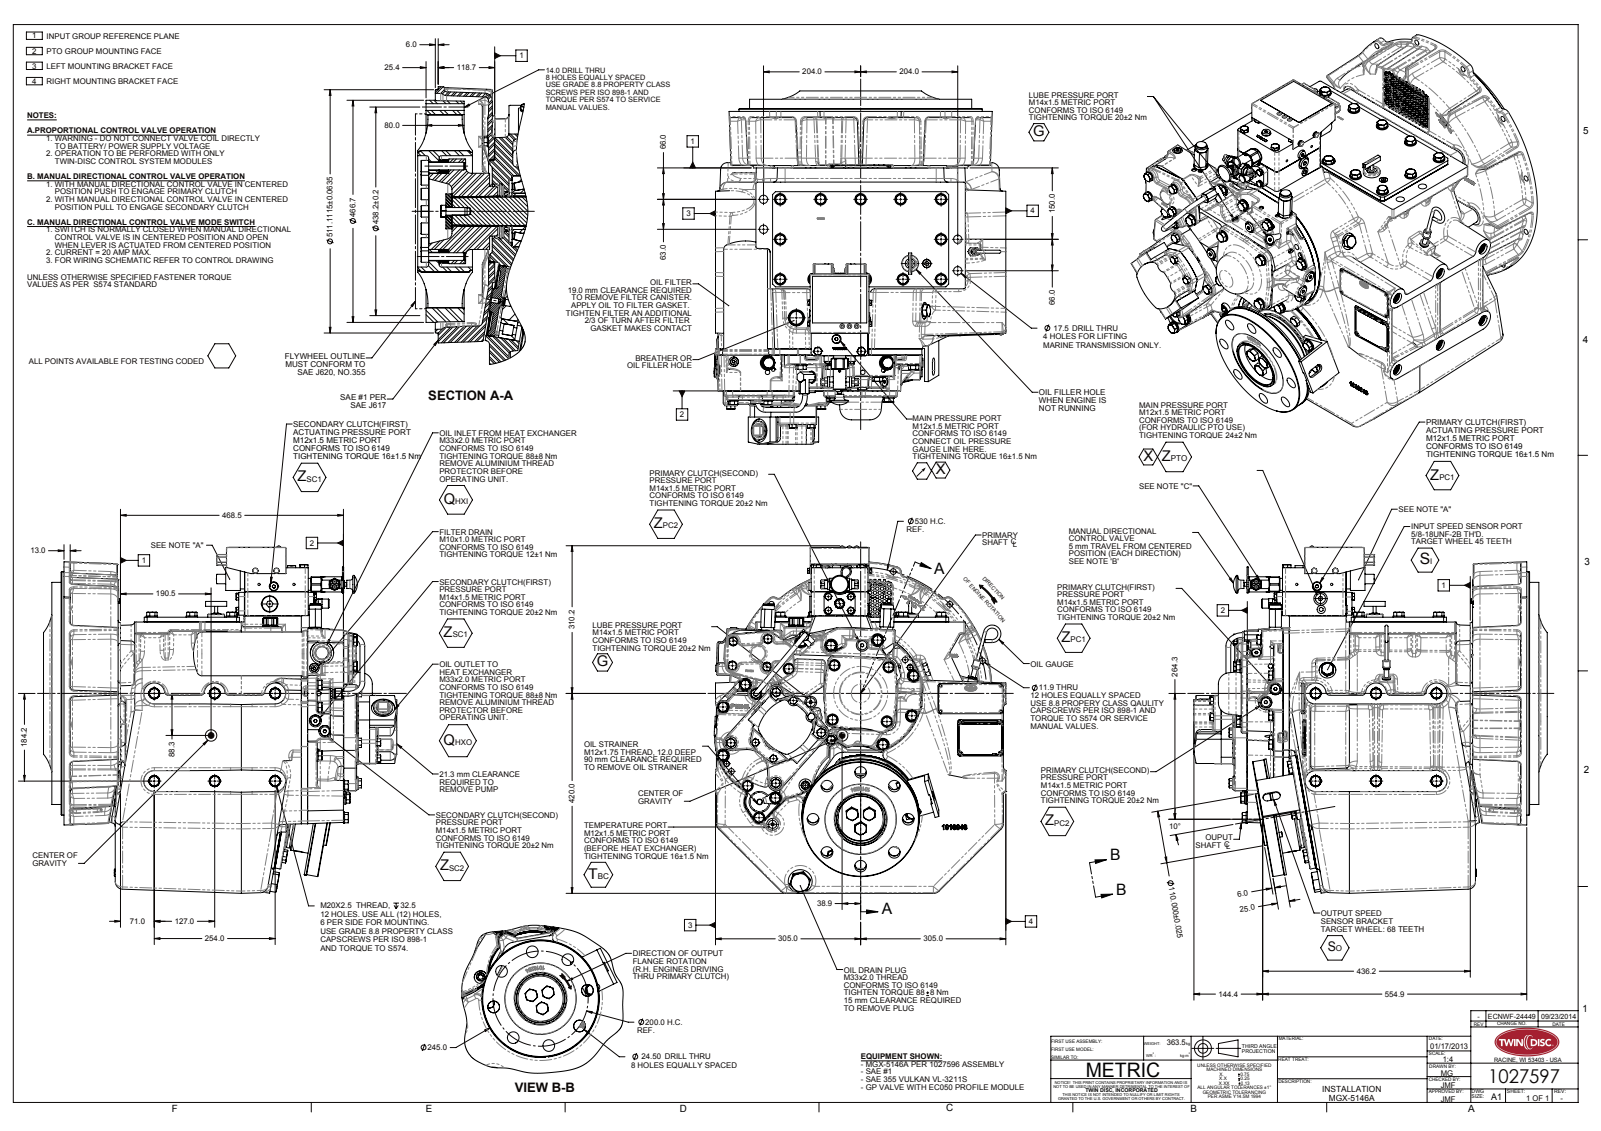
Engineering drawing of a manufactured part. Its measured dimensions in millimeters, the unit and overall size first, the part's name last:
Units: millimetres
Overall size (bounding box): 742.31 × 730.22 × 615.4
Round holes (diameter × count): ⌀7 ×74, ⌀11.91 ×12, ⌀14 ×12, ⌀13 ×10, ⌀12 ×8, ⌀24.5 ×8, ⌀9 ×7, ⌀25 ×7, ⌀4 ×6, ⌀23.51 ×6, ⌀10 ×5, ⌀20 ×5
Round bosses / shafts (diameter × count): ⌀24 ×47, ⌀12 ×12, ⌀10 ×9, ⌀19 ×8, ⌀19.85 ×5, ⌀16 ×5, ⌀2.54 ×5, ⌀17 ×4
Partial cylindrical surfaces — rounded edges, fillets, slot ends (radius × count): R3 ×101, R0.25 ×75, R8 ×73, R6.5 ×71, R2.5 ×54, R1.02 ×33, R16 ×32, R2 ×28
Main face-to-face distances: 0.39, 13.09, 404.48, 404.09, 75, 75.39, 479.48, 88.48, 13.48, 391
Hole centre spacings: 100, 459.05, 26.51, 141.42, 76.54, 20.07, 30, 52.94
Bodies: 0 solids, 7163 faces (2370 planar, 2027 cylindrical, 2766 other)
Part name (STEP PRODUCT): 1027597
STEP written by: SolidWorks 2010 (AUTOMOTIVE_DESIGN)
